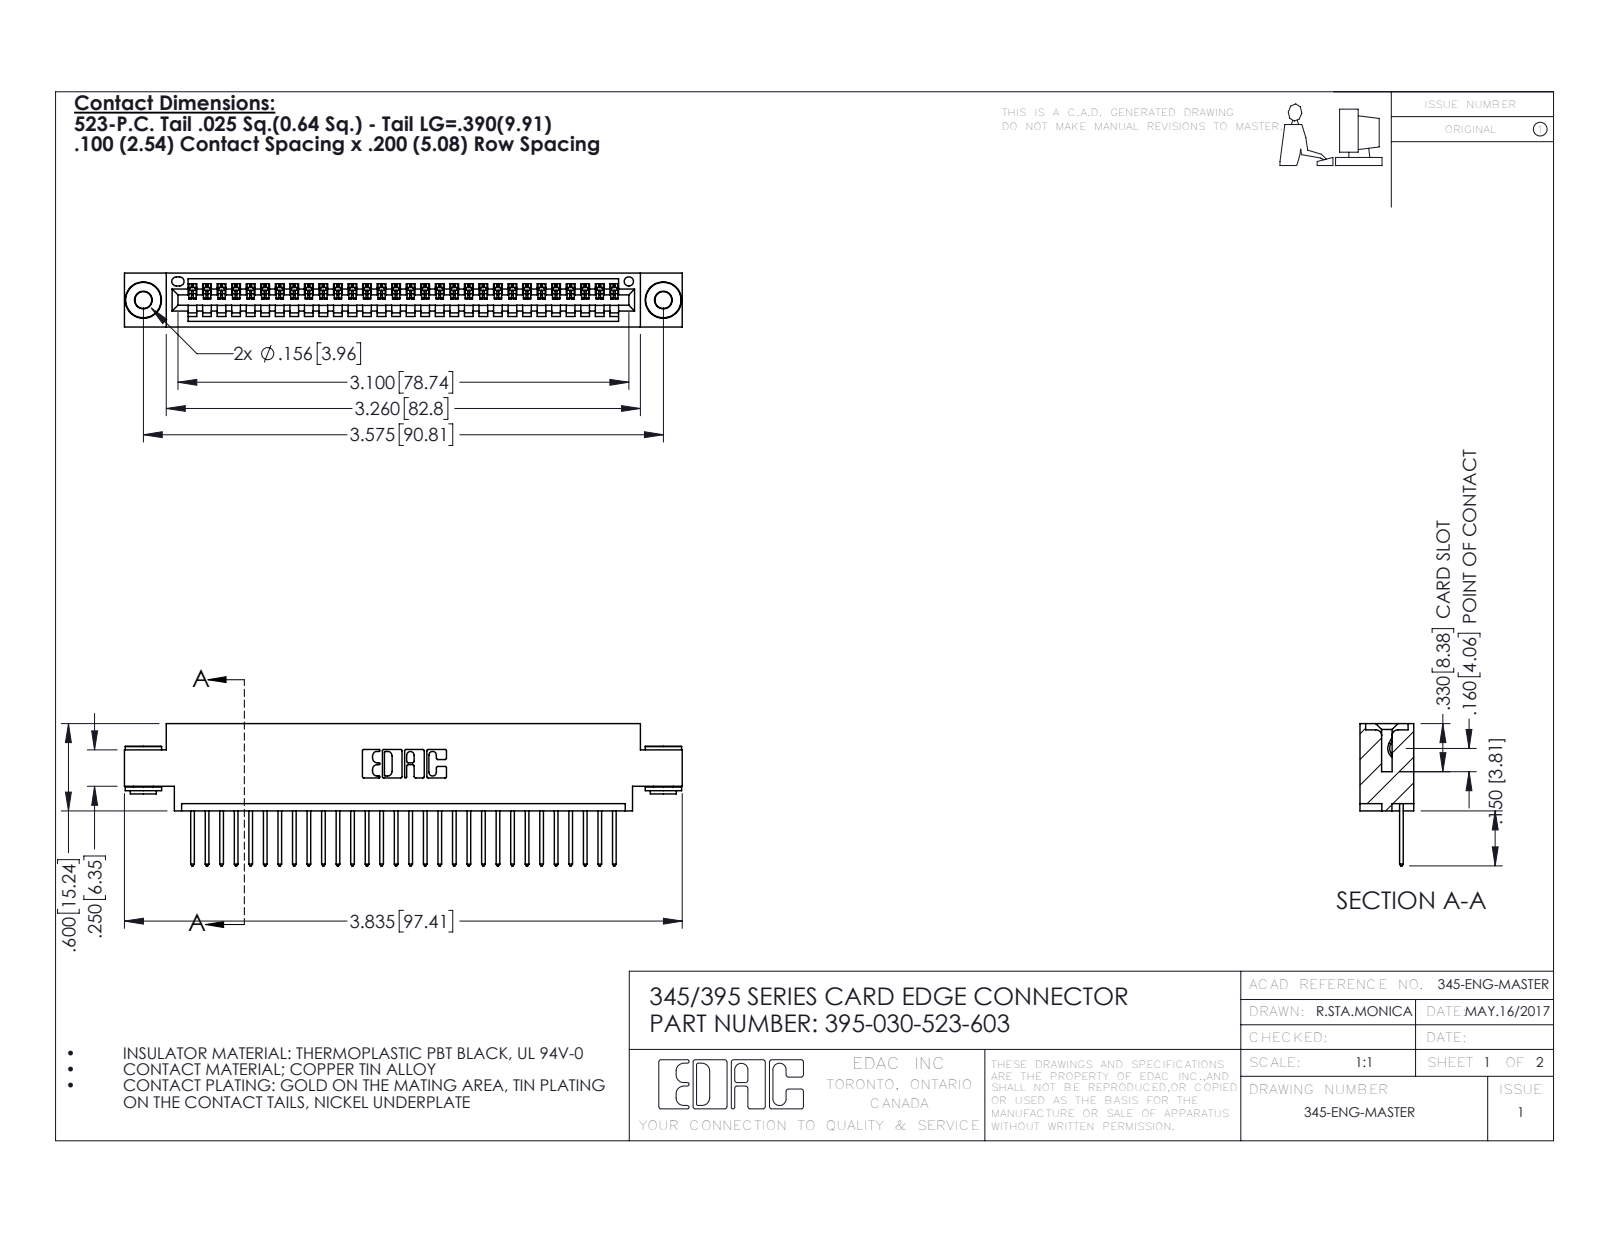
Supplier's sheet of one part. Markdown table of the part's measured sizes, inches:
| quantity | value |
| --- | --- |
| part name | 395-030-523-603; 345 Part_0.170 Offset - 0.156 Dia-TH; 345-292-001_345-293-123; 345-250-002_345-250-002-102 |
| STEP written by | SolidWorks 2016 (CONFIG_CONTROL_DESIGN) |
| units | inches |
| bodies | 33 solids, 1908 faces (1294 planar, 606 cylindrical, 8 other) |
| overall size | 3.835 × 0.977 × 0.37 |
| volume | 0.552 in³ |
| surface area | 18.96 in² |
| round holes (diameter × count) | 0.116 × 2, 0.156 × 2, 0.064 × 1 |
| round bosses / shafts (diameter × count) | 0.25 × 2, 0.18 × 2, 0.136 × 2 |
| partial cylindrical surfaces (radius × count) | 0.006 × 60, 0.01 × 60, 0.01 × 22, 0.007 × 6, 0.031 × 6, 0.026 × 3, 0.031 × 2, 0.04 × 2 |
| main face-to-face distances | 0.072, 0.298, 0.37, 0.2, 0.098, 0.272, 0.025, 0.225, 0.175, 0.149 |
| hole center spacings | 0.27, 3.34, 3.575 |
